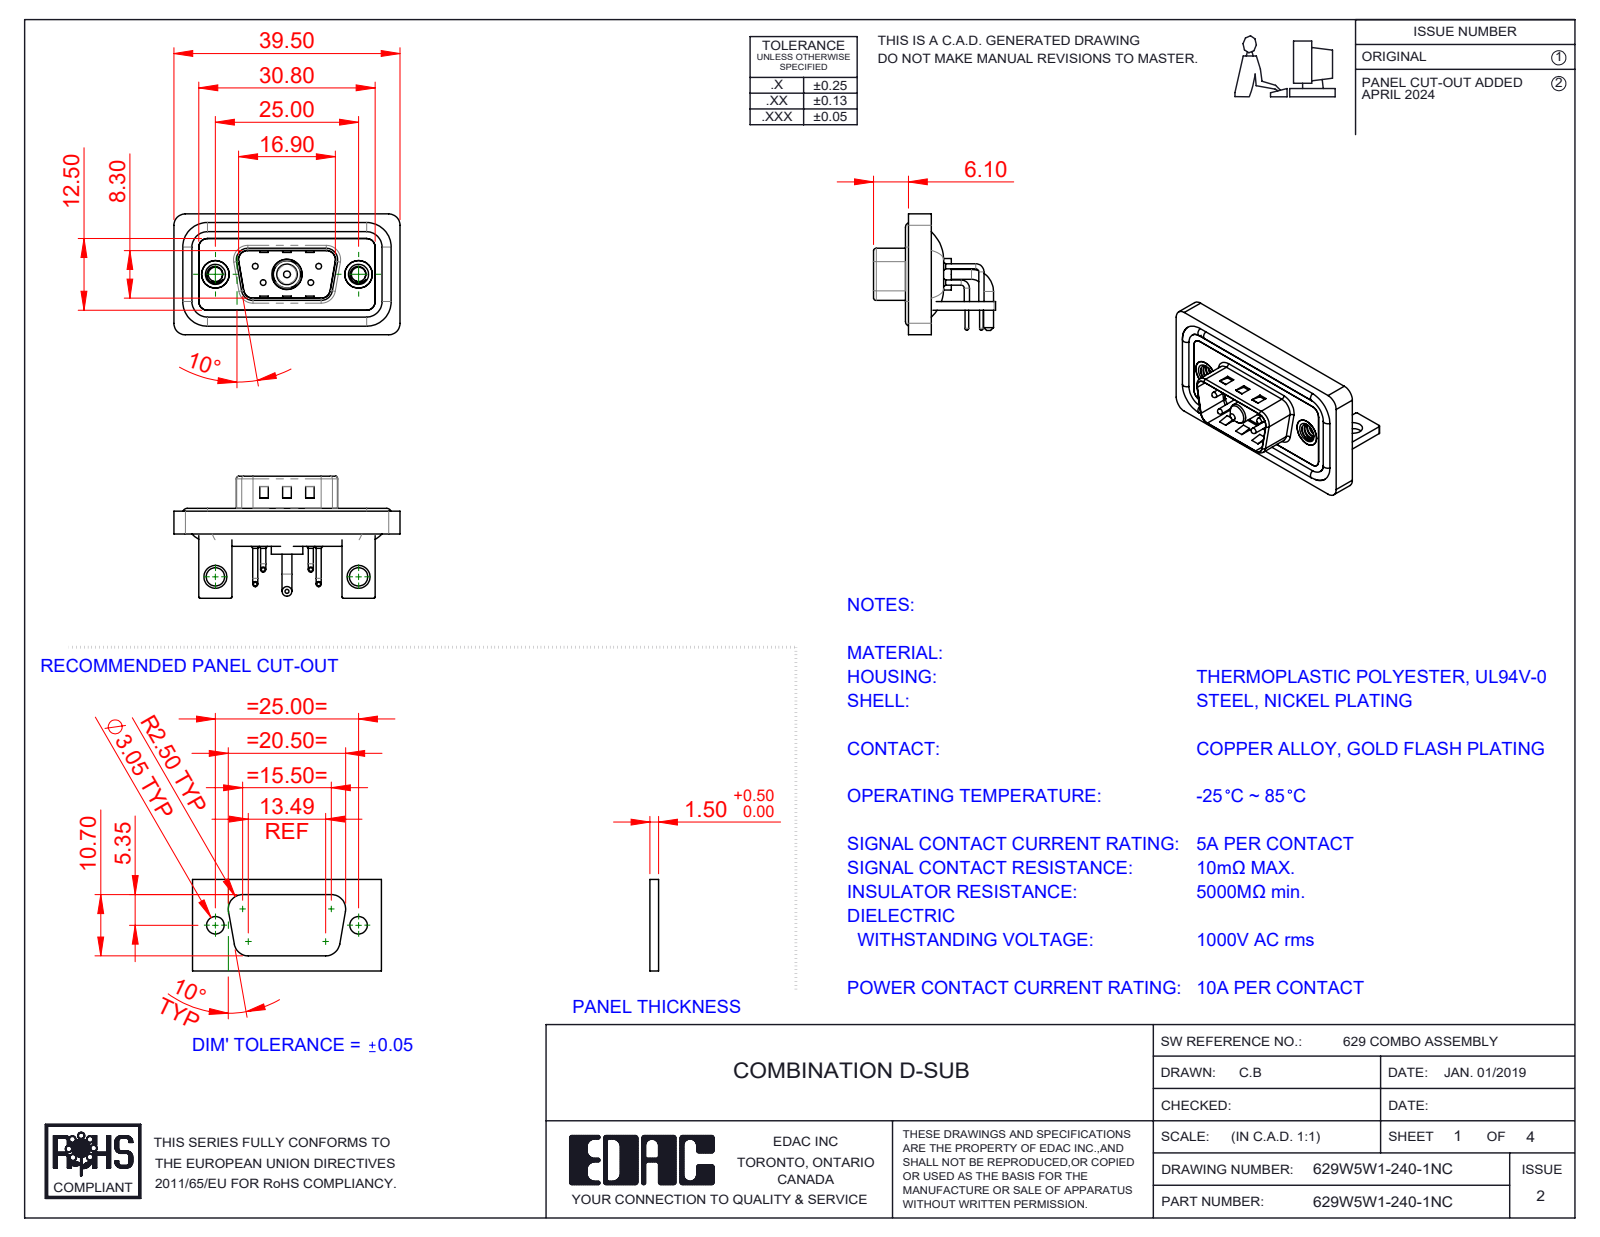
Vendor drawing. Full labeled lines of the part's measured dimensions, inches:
Part name (STEP PRODUCT): 629Combo Threaded Rivet_B; Power Pin_10A RA; 629Combo Shell Front_09 Contacts; 629Combo Housing_5W1 (+6 more)
STEP written by: SolidWorks 2023 (CONFIG_CONTROL_DESIGN)
Units: inches
Bodies: 15 solids, 932 faces (431 planar, 363 cylindrical, 138 other)
Overall size (bounding box): 1.555 × 0.839 × 0.831
Volume: 0.286 in³ · Surface area: 11.94 in²
Round holes (diameter × count): ⌀0.03 ×4, ⌀0.063 ×4, ⌀0.079 ×4, ⌀0.098 ×2, ⌀0.126 ×2, ⌀0.157 ×2, ⌀0.189 ×2, ⌀0.197 ×2, ⌀0.191 ×1, ⌀0.209 ×1
Round bosses / shafts (diameter × count): ⌀0.035 ×8, ⌀0.063 ×4, ⌀0.059 ×4, ⌀0.039 ×4, ⌀0.026 ×4, ⌀0.193 ×2, ⌀0.067 ×2, ⌀0.217 ×1
Partial cylindrical surfaces — rounded edges, fillets, slot ends (radius × count): R0.079 ×19, R0.059 ×18, R0.01 ×16, R0.02 ×9, R0.063 ×8, R0.024 ×4, R0.026 ×4, R0.035 ×4
Main face-to-face distances: 0.016, 0.059, 0.031, 0.114, 0.043, 0.083, 0.047, 0.063, 0.098, 0.146
Hole centre spacings: 0.124, 0.225, 0.28, 0.492, 0.713, 0.984, 0.173, 0.173
